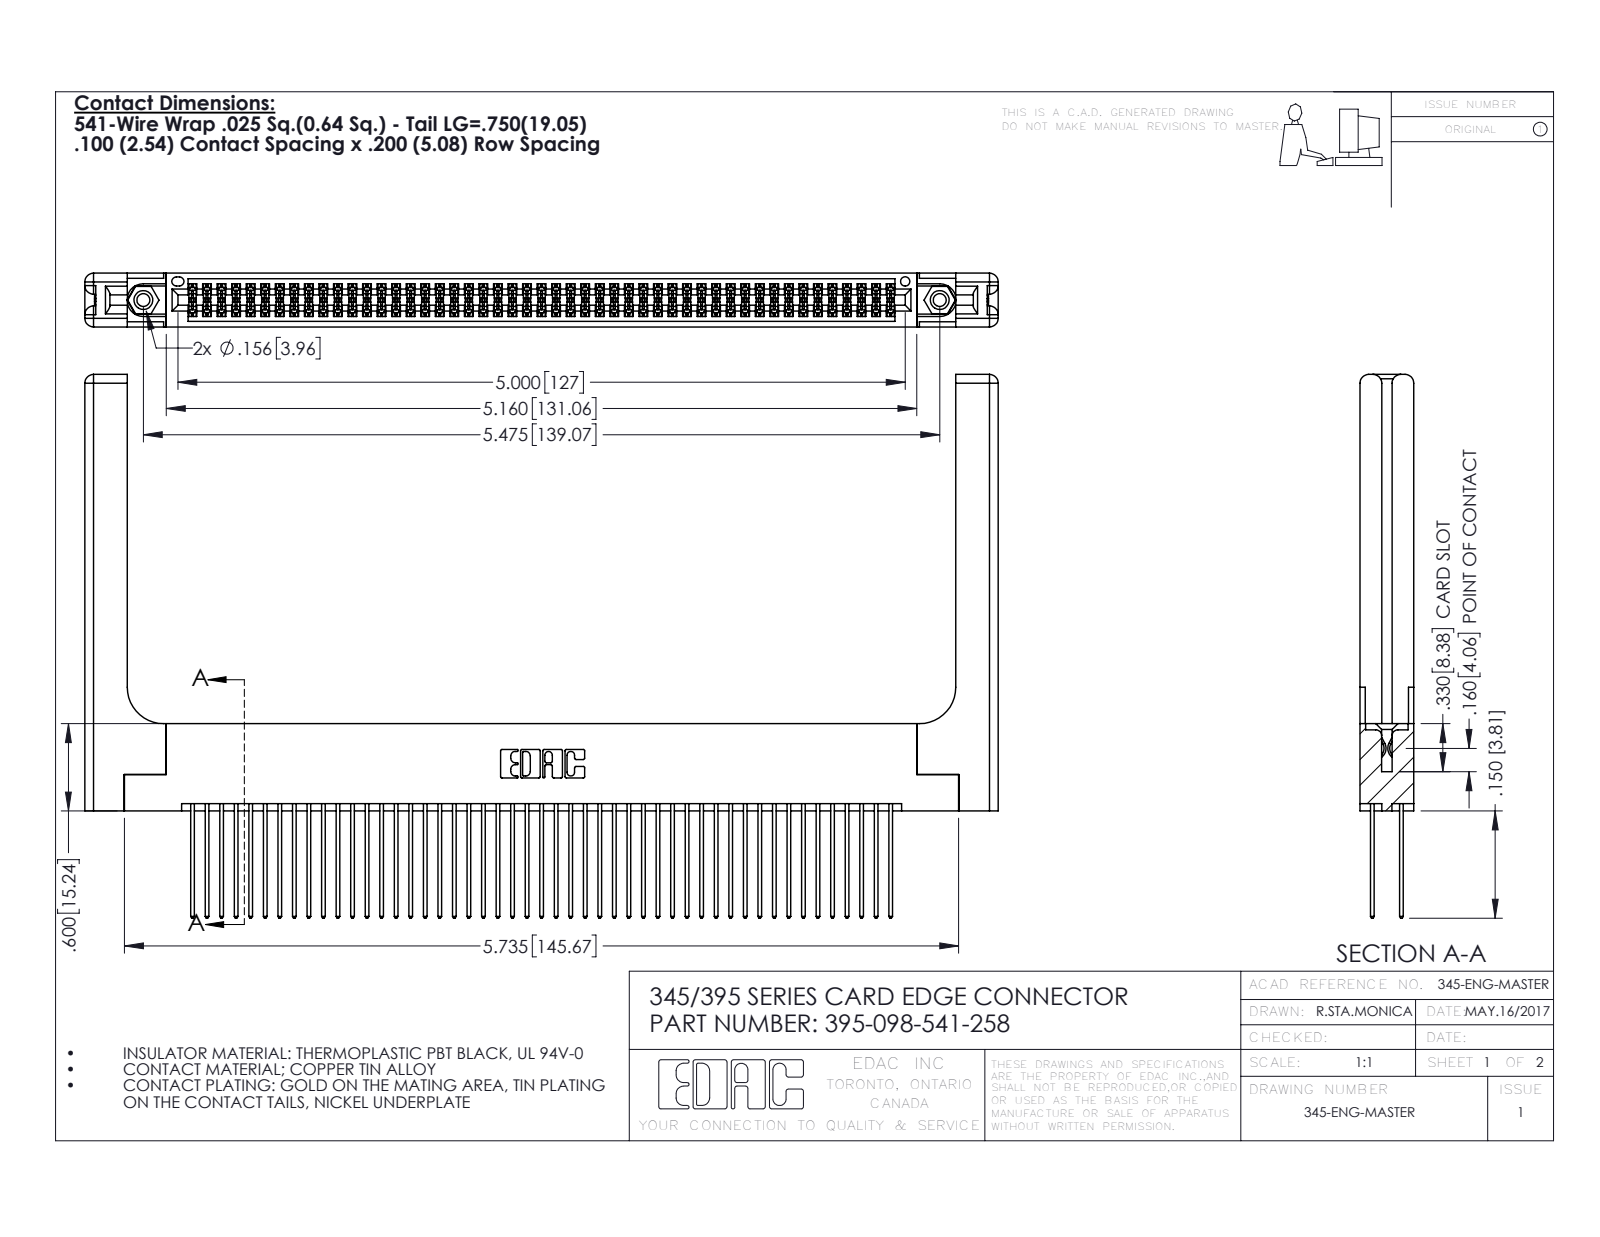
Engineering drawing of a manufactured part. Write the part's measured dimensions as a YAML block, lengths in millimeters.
part_name: "345-250-001_345-250-001-102; 345-220-058_345-220-058; 345 Part_Flush Mounting Lugs - 0.156 Dia-TH; 345-292-001_345-293-141 (+1 more)"
step_written_by: "SolidWorks 2016 (CONFIG_CONTROL_DESIGN)"
units: millimeters
bodies: {solids: 103, faces: 5282, planar: 3462, cylindrical: 1760, other: 60}
overall_size: [159.5, 94.9, 9.4]
volume: 24600
surface_area: 31660
round_holes:
  - {diameter: 2.3, count: 2}
  - {diameter: 3.2, count: 2}
  - {diameter: 4, count: 2}
  - {diameter: 1.6, count: 1}
round_bosses_or_shafts:
  - {diameter: 3.9, count: 2}
partial_cylinders:
  - {radius: 0.2, count: 147}
  - {radius: 0.3, count: 98}
  - {radius: 0.3, count: 22}
  - {radius: 1.5, count: 16}
  - {radius: 0.2, count: 6}
  - {radius: 0.8, count: 6}
  - {radius: 0.7, count: 3}
  - {radius: 0.4, count: 2}
face_to_face_distances: [1.8, 7.6, 5.1, 9.4, 2.5, 6.9, 0.6, 5.7, 4.4, 3.8]
hole_center_spacings: [6.9, 133.1, 139.1]
